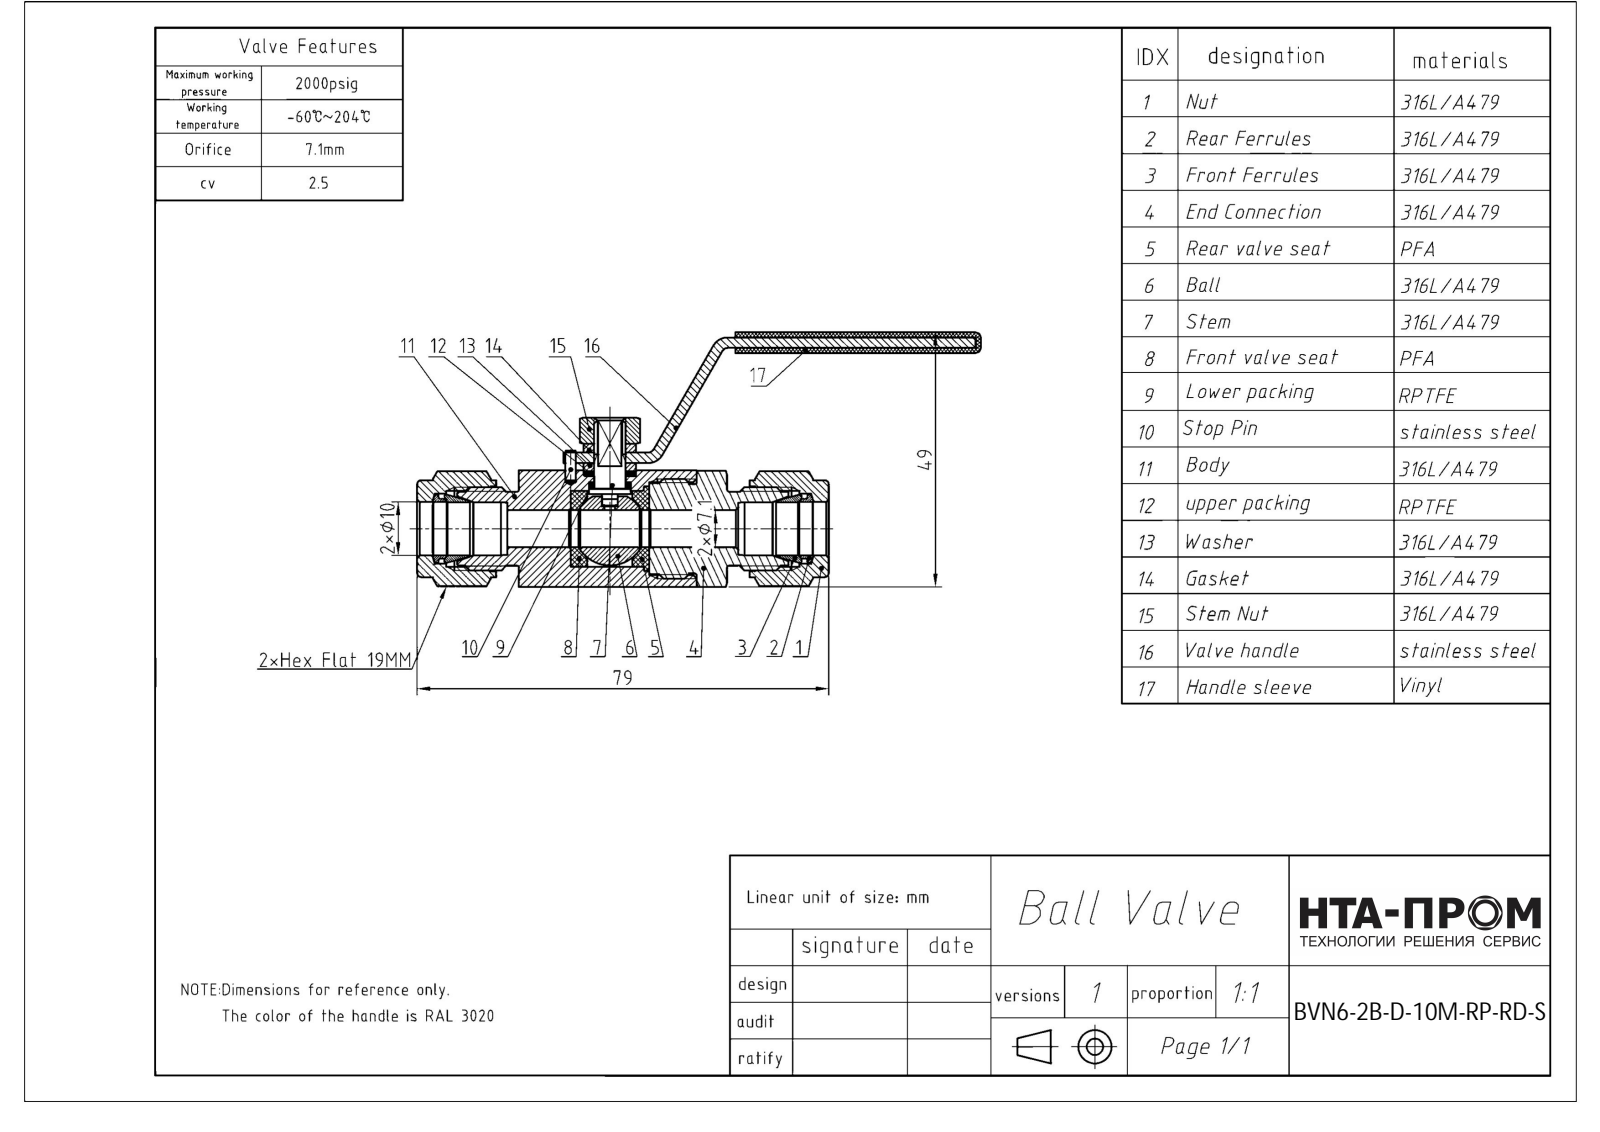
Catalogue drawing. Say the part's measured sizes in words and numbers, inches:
The part is named "BVN6-2B-D-10M-RP-RD-S; BVN6; BVN6-2B-D-10M-RP-RD-S001; COMPOUND (+1 more)". Its 3-D file was written by "FreeCAD (AUTOMOTIVE_DESIGN)". It is 5 solids with 203 faces: 72 planar, 60 cylindrical and 71 other. Overall it measures 4.203 by 1.875 by 1.011 inches. Its volume is 1.614 cubic inches and its surface area 21.41 square inches. Round holes: 1 of diameter 0.28, 1 of diameter 0.399, 1 of diameter 0.4, 1 of diameter 0.401, 1 of diameter 0.484. Round bosses or shafts: 2 of diameter 0.079, 1 of diameter 0.728, 1 of diameter 0.555, 1 of diameter 0.394, 1 of diameter 0.315, 1 of diameter 0.236, 1 of diameter 0.118. Partial cylindrical surfaces (rounded edges, fillets, slot ends): 6 of radius 0.02, 4 of radius 0.039, 4 of radius 0.118, 2 of radius 0.197, 1 of radius 0.236, 1 of radius 0.354, 1 of radius 0.432. The main face-to-face distances are 0.875, 0.063, 0.813, 0.079, 0.75, 0.921, 1, 1.796, 1.875, 0.866.
